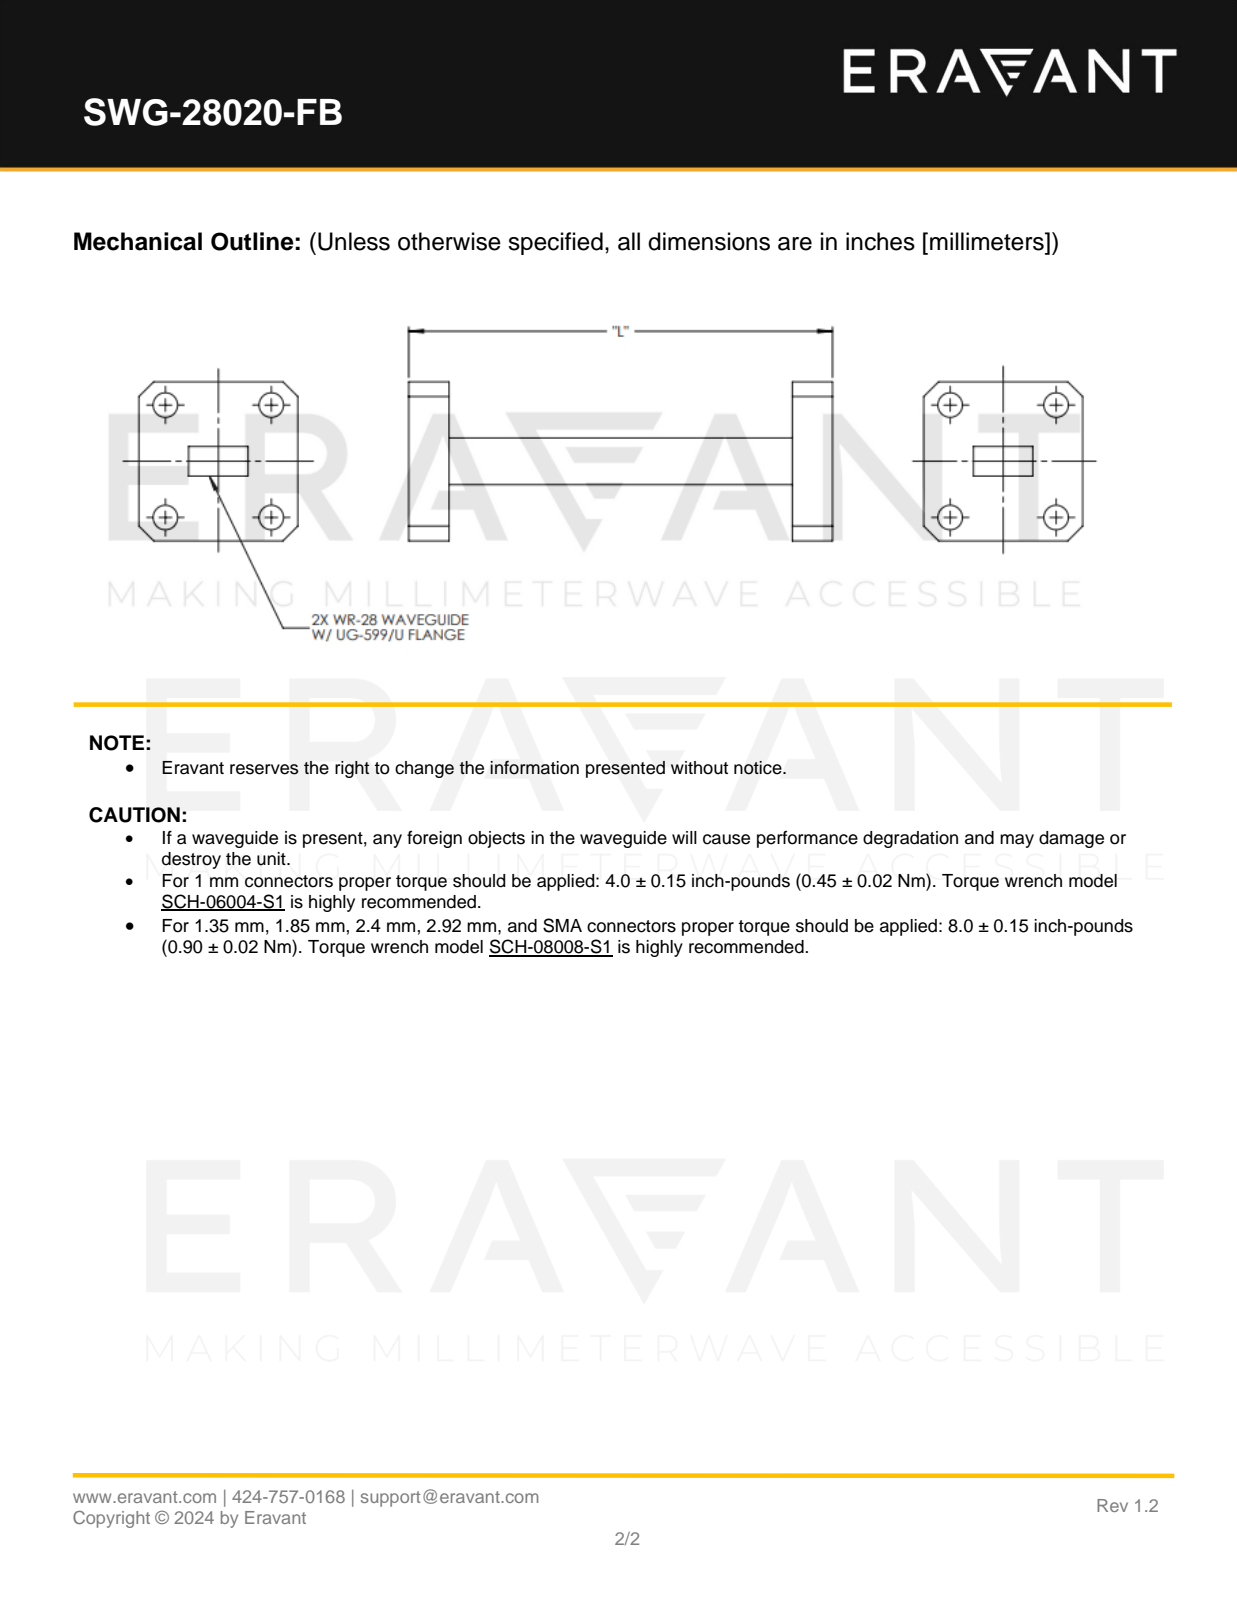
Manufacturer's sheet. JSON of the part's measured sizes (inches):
{"part_name": "SWG-28020-FB", "step_written_by": "SolidWorks 2013 (CONFIG_CONTROL_DESIGN)", "units": "inches", "bodies": {"solids": 1, "faces": 44, "planar": 28, "cylindrical": 16, "other": 0}, "overall_size": [2, 0.75, 0.75], "volume_in3": 0.244, "surface_area_in2": 6.996, "round_holes": [[0.116, 4]], "face_to_face_distances": [0.04, 0.18, 0.19, 1.81, 0.22, 0.14, 0.32, 2, 1.62, 0.36], "hole_center_spacings": [0.5, 0.53, 0.729]}
